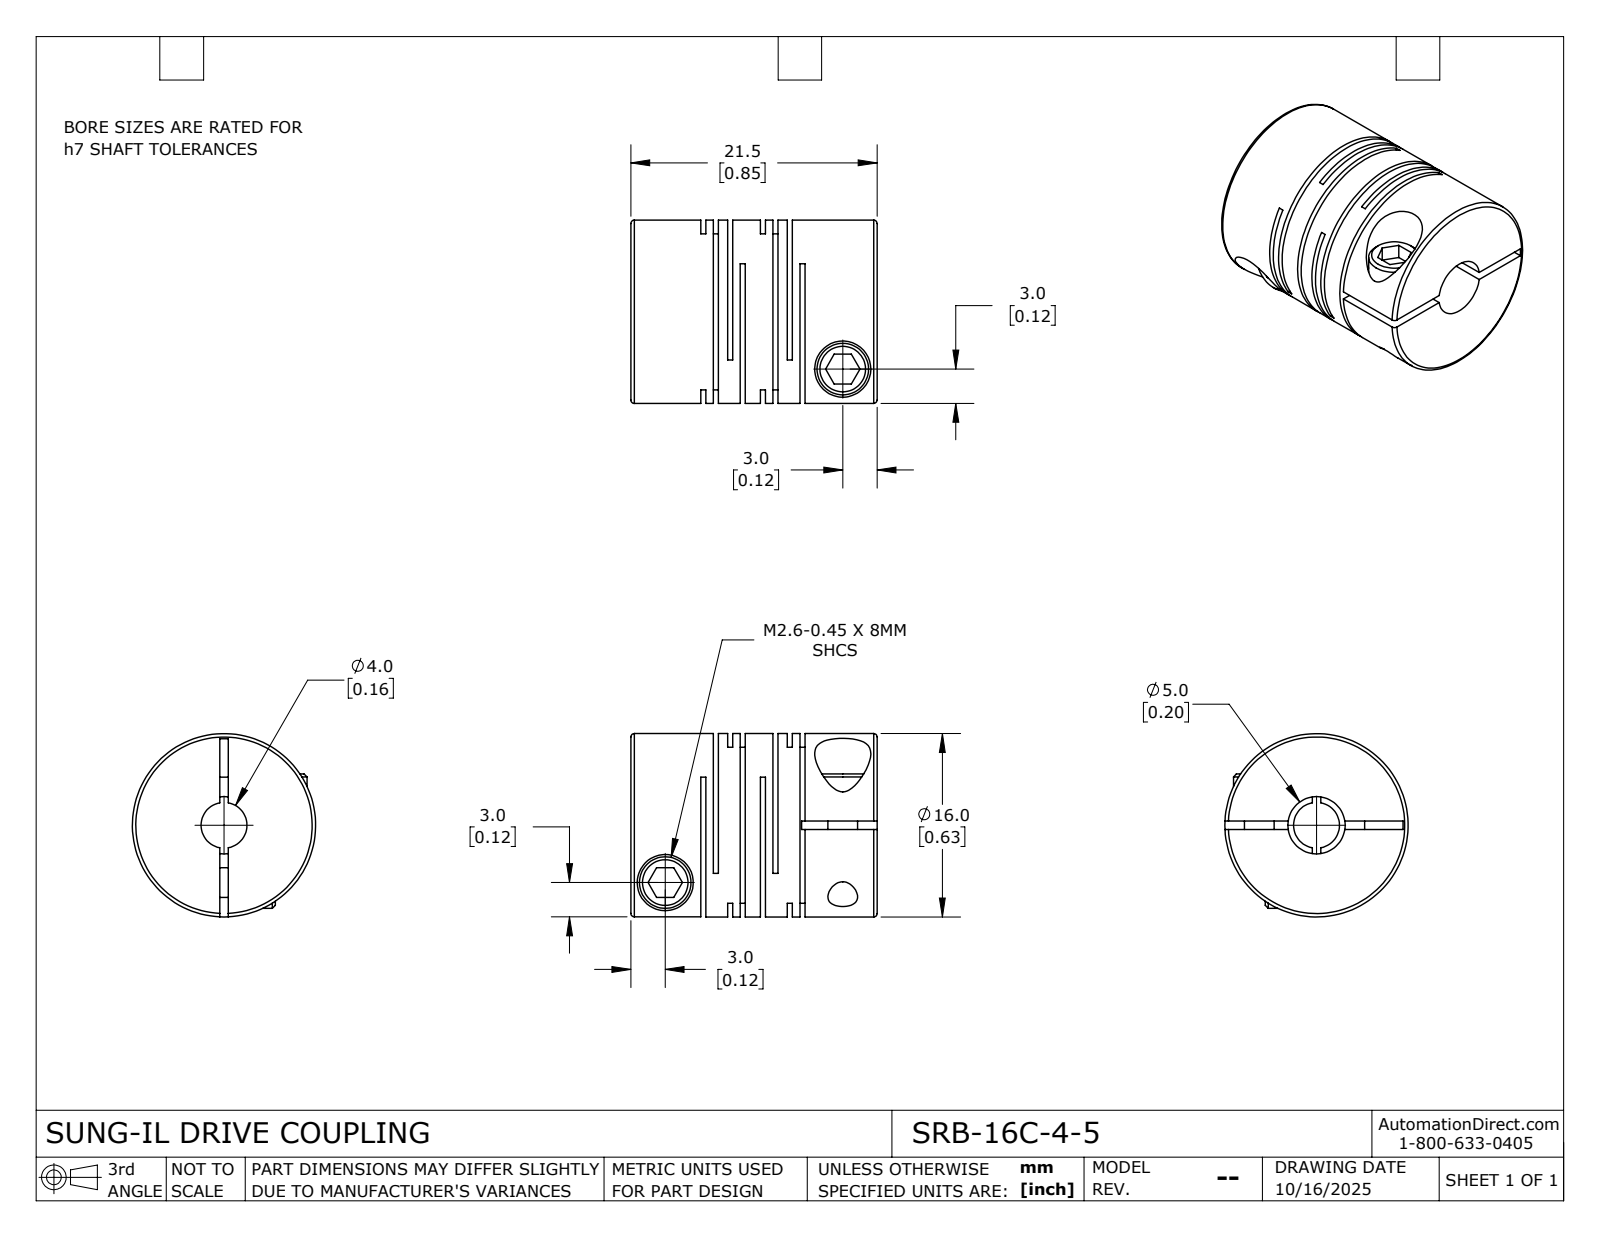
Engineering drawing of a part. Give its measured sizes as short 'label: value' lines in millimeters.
name: SRB-16C-4-5
written by: SolidWorks 2024 (CONFIG_CONTROL_DESIGN)
unit: mm
bodies: 1 solid, 115 faces (60 planar, 42 cylindrical, 13 other)
size: 21.5 × 16 × 16
volume: 3 236 mm³; area: 4 370 mm²
holes: 2× ⌀2.6, 2× ⌀4.9, 1× ⌀4, 1× ⌀5
bosses: 2× ⌀4.5, 1× ⌀16
face distances: 0.44, 1.1, 5.21, 2.35, 0.66, 1.91, 4.77, 1.25, 4.11, 2.86
